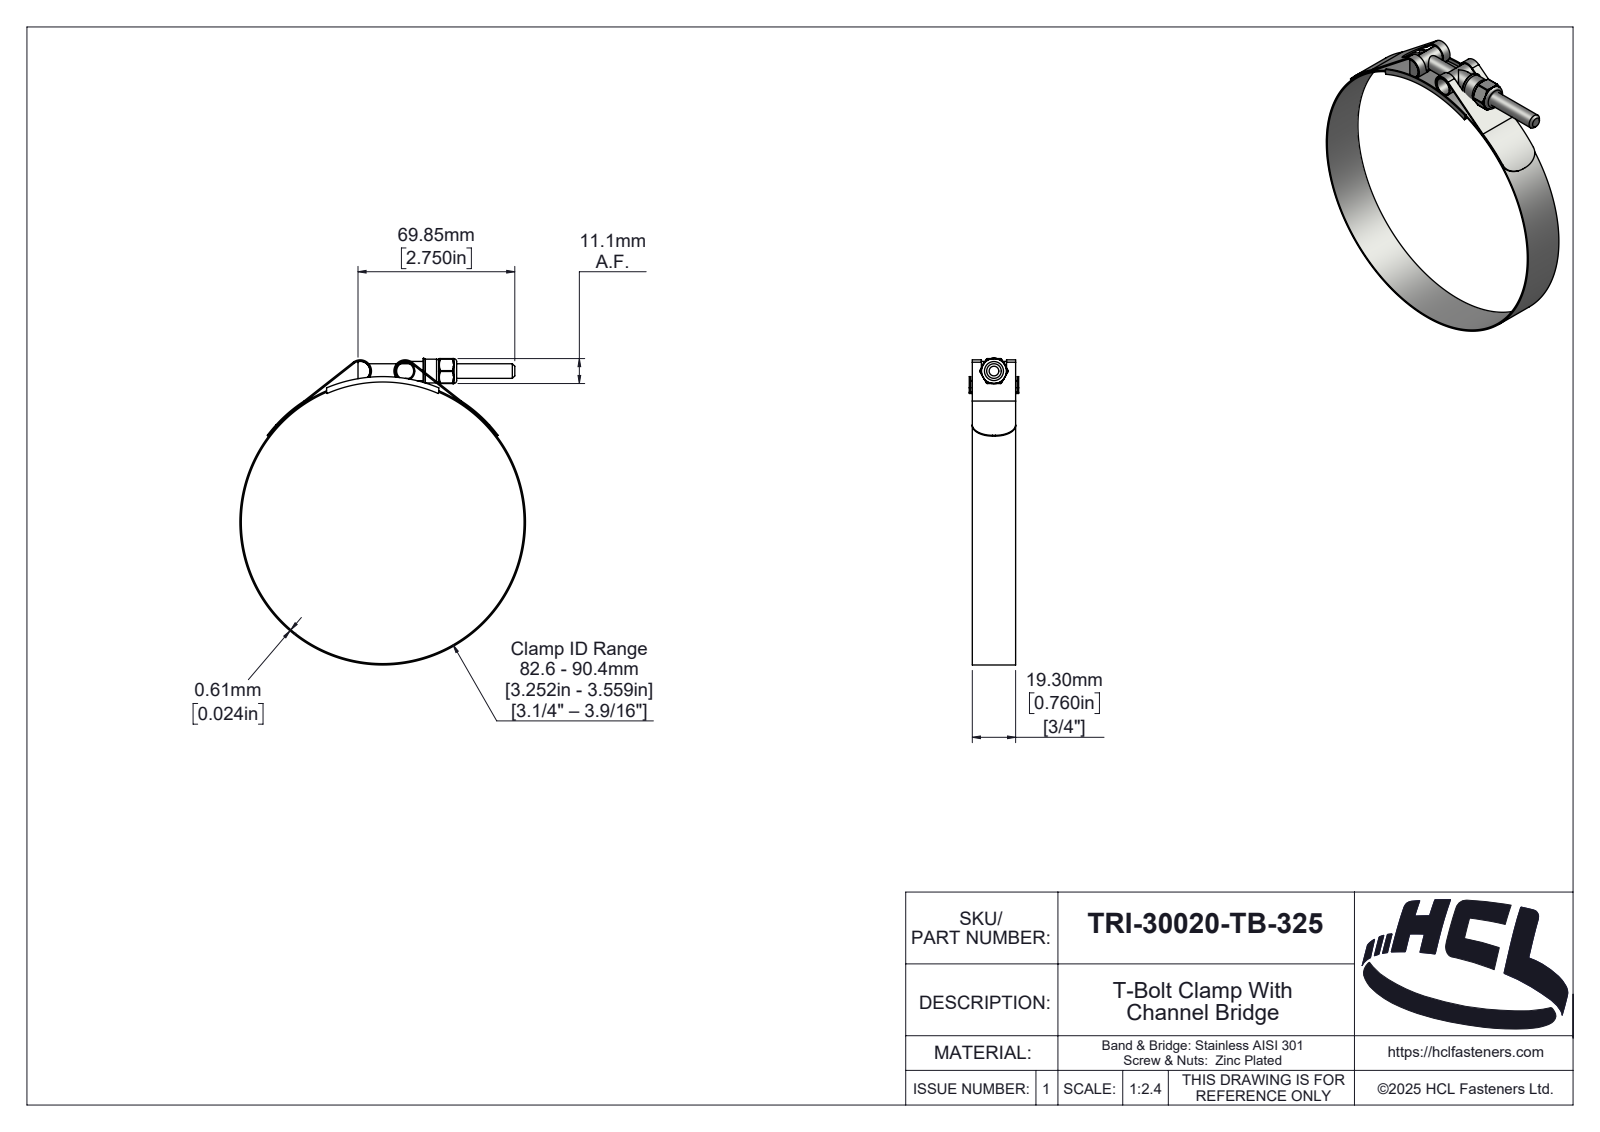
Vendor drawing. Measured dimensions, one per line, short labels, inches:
name: TRI-30020-TB-325
written by: SolidWorks 2025 (AUTOMOTIVE_DESIGN)
unit: in
bodies: 6 solids, 330 faces (44 planar, 122 cylindrical, 164 other)
size: 5.378 × 5.009 × 0.866
volume: 0.65 in³; area: 40.83 in²
holes: 1× ⌀0.213, 1× ⌀0.25, 1× ⌀0.256, 1× ⌀0.298, 1× ⌀4.961
bosses: 2× ⌀0.338, 1× ⌀5.009, 1× ⌀0.417
rounds: 6× R0.015, 2× R0.02, 2× R0.173, 2× R0.197, 1× R0.023, 1× R0.095, 1× R0.119, 1× R0.126
face distances: 0.024, 0.76, 0.053, 0.813, 0.029, 0.842, 0.789, 0.866, 0.438, 0.818
hole spacings: 2.677
